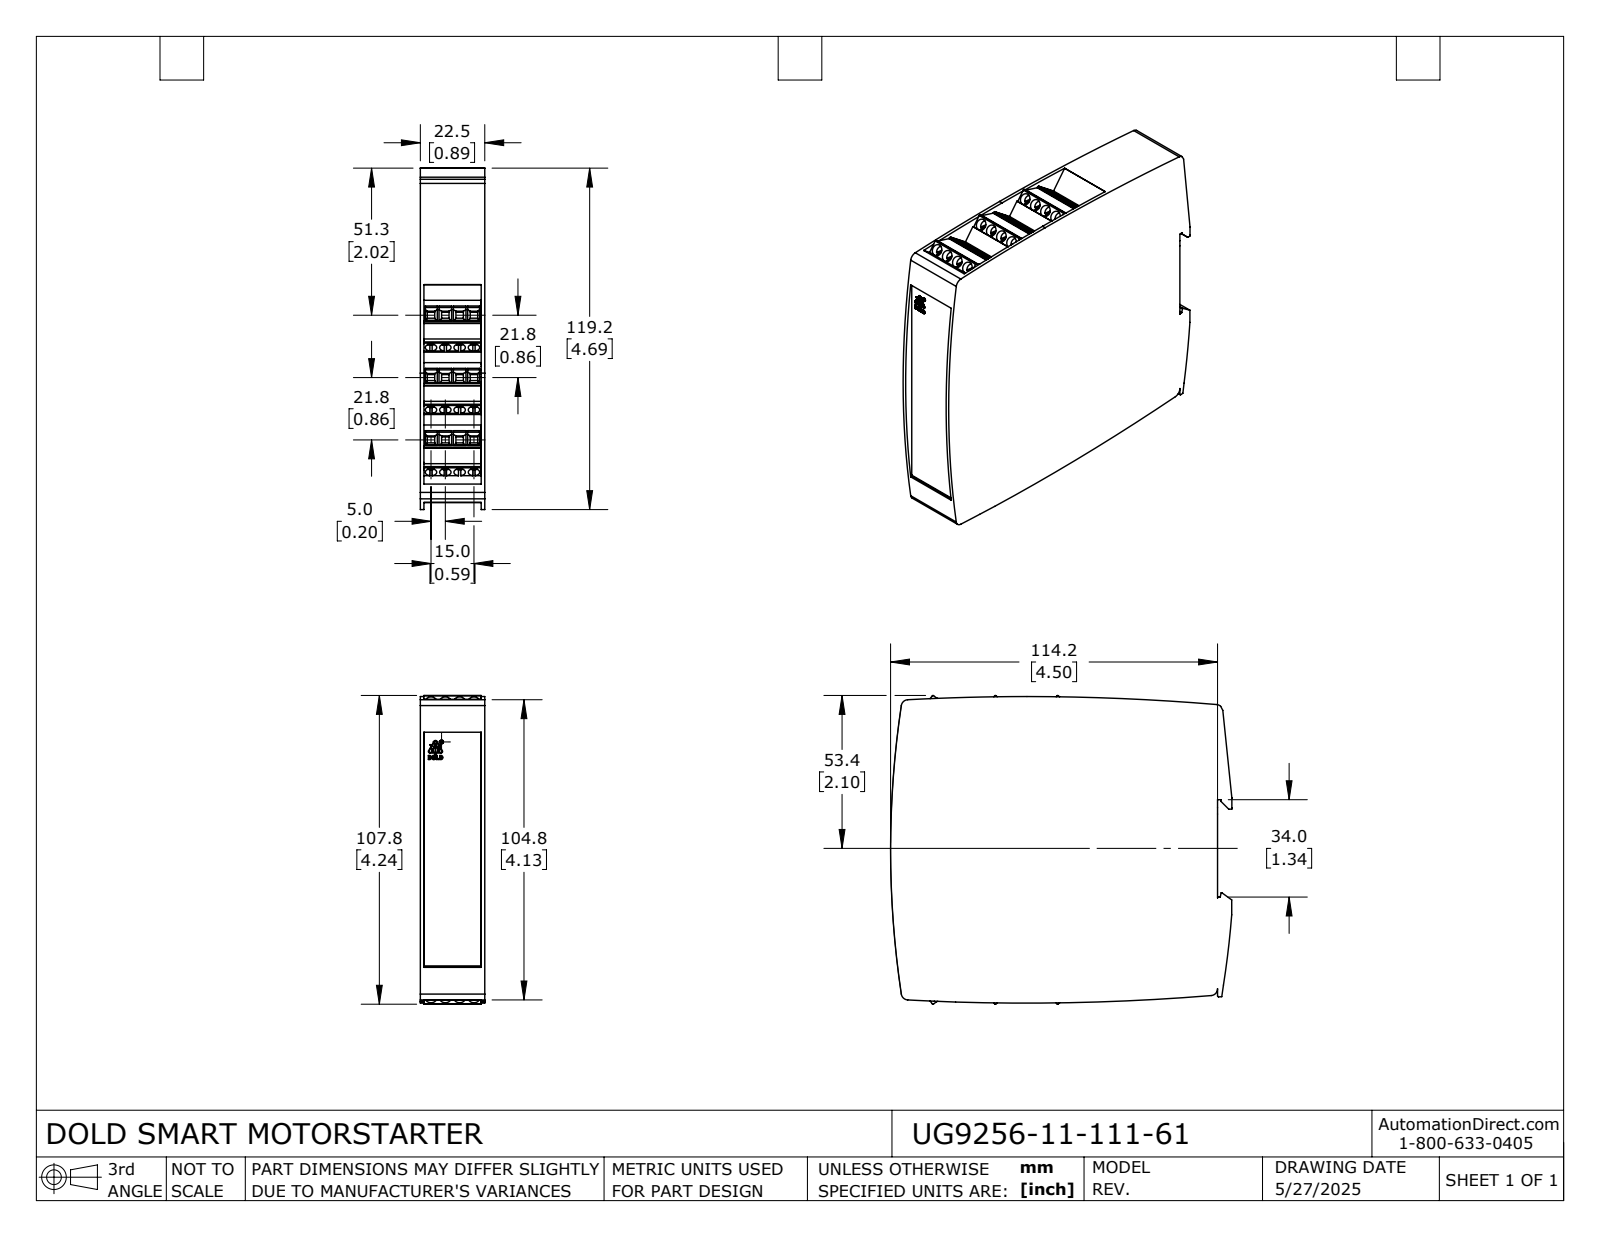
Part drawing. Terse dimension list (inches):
name: UG9256-11-111-61
written by: SolidWorks 2024 (AUTOMOTIVE_DESIGN)
unit: in
bodies: 1 solid, 1036 faces (813 planar, 222 cylindrical, 1 other)
size: 4.693 × 4.243 × 0.886
volume: 15.85 in³; area: 64.72 in²
holes: 24× ⌀0.157, 1× ⌀0.053
bosses: 24× ⌀0.15, 1× ⌀0.049
rounds: 15× R0.012, 14× R0.02, 12× R0.004, 7× R0.094, 6× R0.005, 4× R0.004, 4× R31.496, 3× R0.021
face distances: 0.886, 0.049, 0.837, 0.675, 4.379, 0.051, 0.835, 1.35, 0.528, 0.785
hole spacings: 0.563, 0.197, 0.528, 0.658, 0.394, 1.073, 0.792, 1.055
